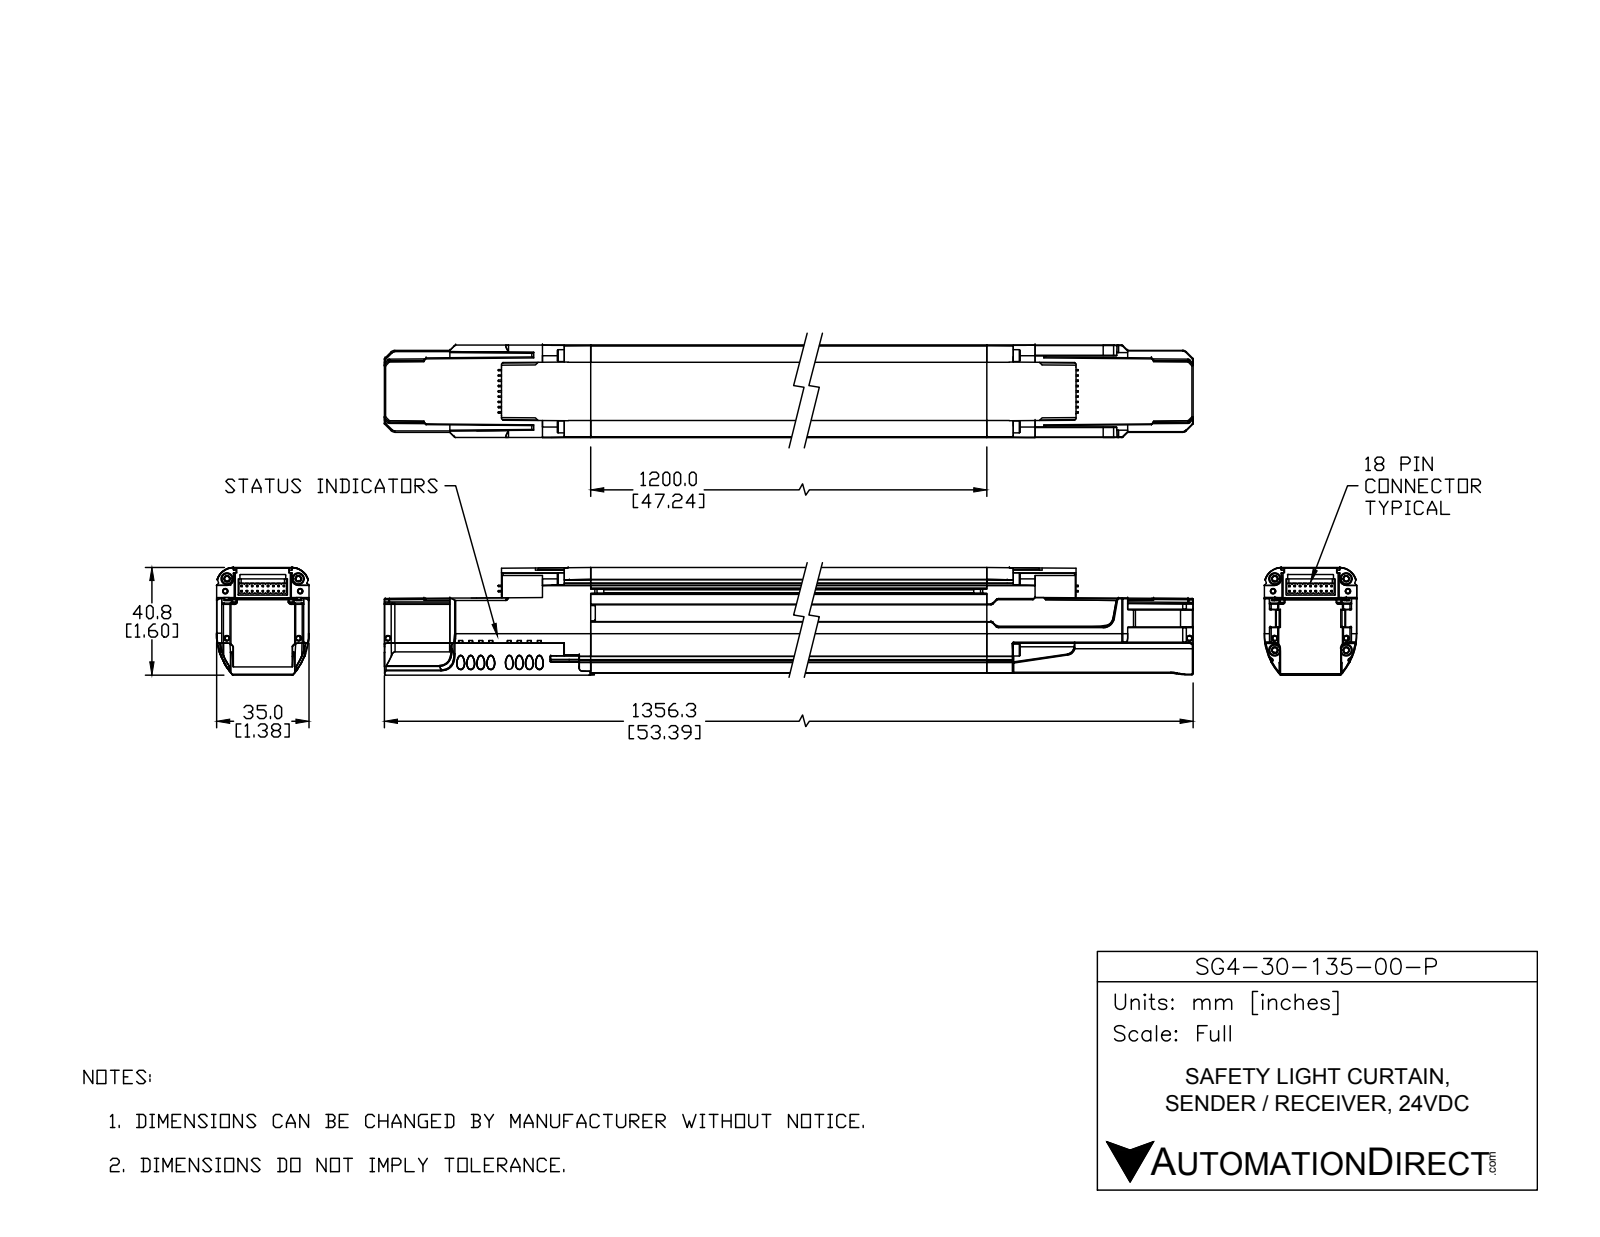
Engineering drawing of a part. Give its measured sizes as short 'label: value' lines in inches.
name: SG4-30-135-OO-P
written by: SolidWorks 2017 (AUTOMOTIVE_DESIGN)
unit: in
bodies: 16 solids, 534 faces (362 planar, 110 cylindrical, 62 other)
size: 53.393 × 2.58 × 2.023
volume: 101.8 in³; area: 563.2 in²
holes: 6× ⌀0.07, 4× ⌀0.1, 4× ⌀0.165, 4× ⌀0.209, 4× ⌀0.26, 1× ⌀0.065, 1× ⌀0.065
bosses: 4× ⌀0.394, 4× ⌀0.197
rounds: 16× R0.106, 8× R0.118, 4× R0.1, 4× R0.11, 2× R0.08, 2× R0.12, 2× R0.123, 2× R0.125
face distances: 0.06, 0.084, 0.024, 1.49, 1.466, 1.55, 1.057, 0.481, 0.985, 1.009
hole spacings: 0.569, 45.665, 0.02, 0.204, 0.207, 0.207, 0.227, 0.71
